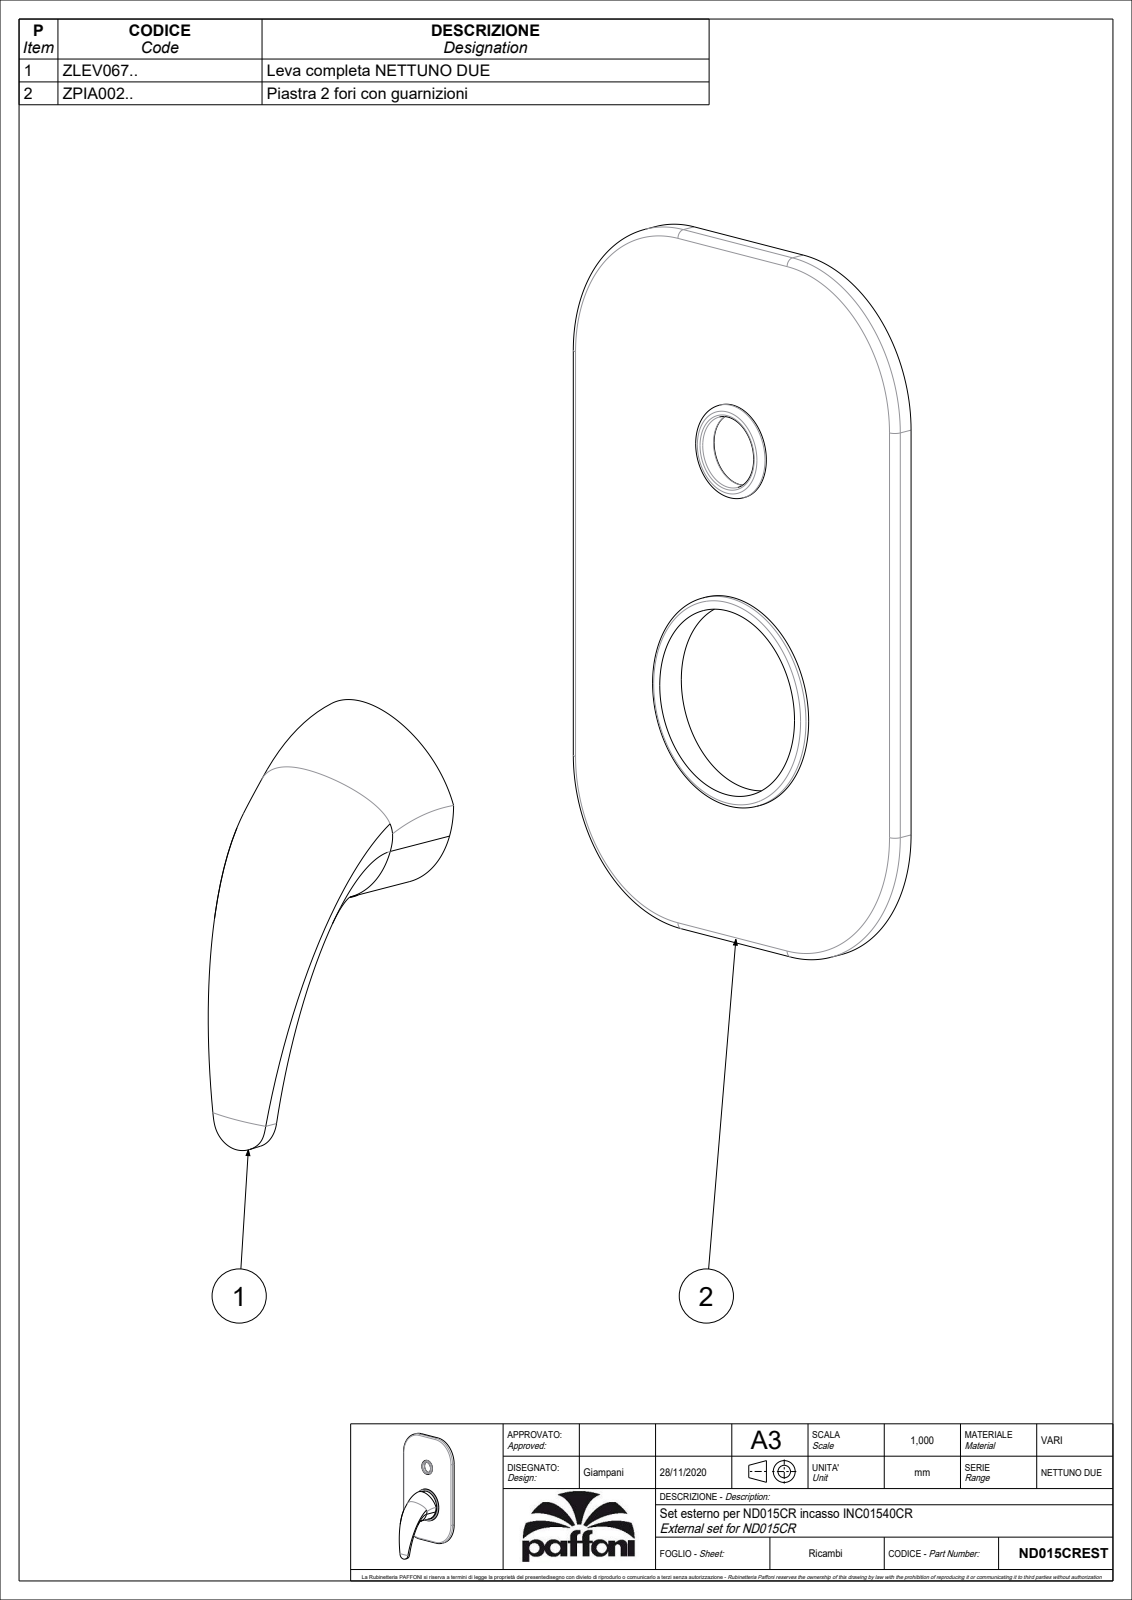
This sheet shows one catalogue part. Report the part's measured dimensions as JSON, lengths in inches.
{"part_name": "ND015CREST", "step_written_by": "CREO PARAMETRIC BY PTC INC, 2020044 (CONFIG_CONTROL_DESIGN)", "units": "inches", "bodies": {"solids": 2, "faces": 145, "planar": 58, "cylindrical": 42, "other": 45}, "overall_size": [8.307, 4.744, 2.559], "volume_in3": 3.762, "surface_area_in2": 98.51, "round_holes": [[0.165, 1], [0.236, 1], [0.37, 1], [0.752, 1], [1.969, 1]], "round_bosses_or_shafts": [[2.224, 1], [2.165, 1], [0.988, 1], [0.925, 1], [0.197, 1]], "partial_cylinders_radius": [[0.047, 4], [0.079, 4], [1.543, 4], [1.575, 4], [0.154, 1], [0.157, 1]], "face_to_face_distances": [0.031, 0.205, 4.713, 0.236, 0.079, 2.071, 2.673, 2.039, 2.642, 0.315], "hole_center_spacings": [2.677]}
